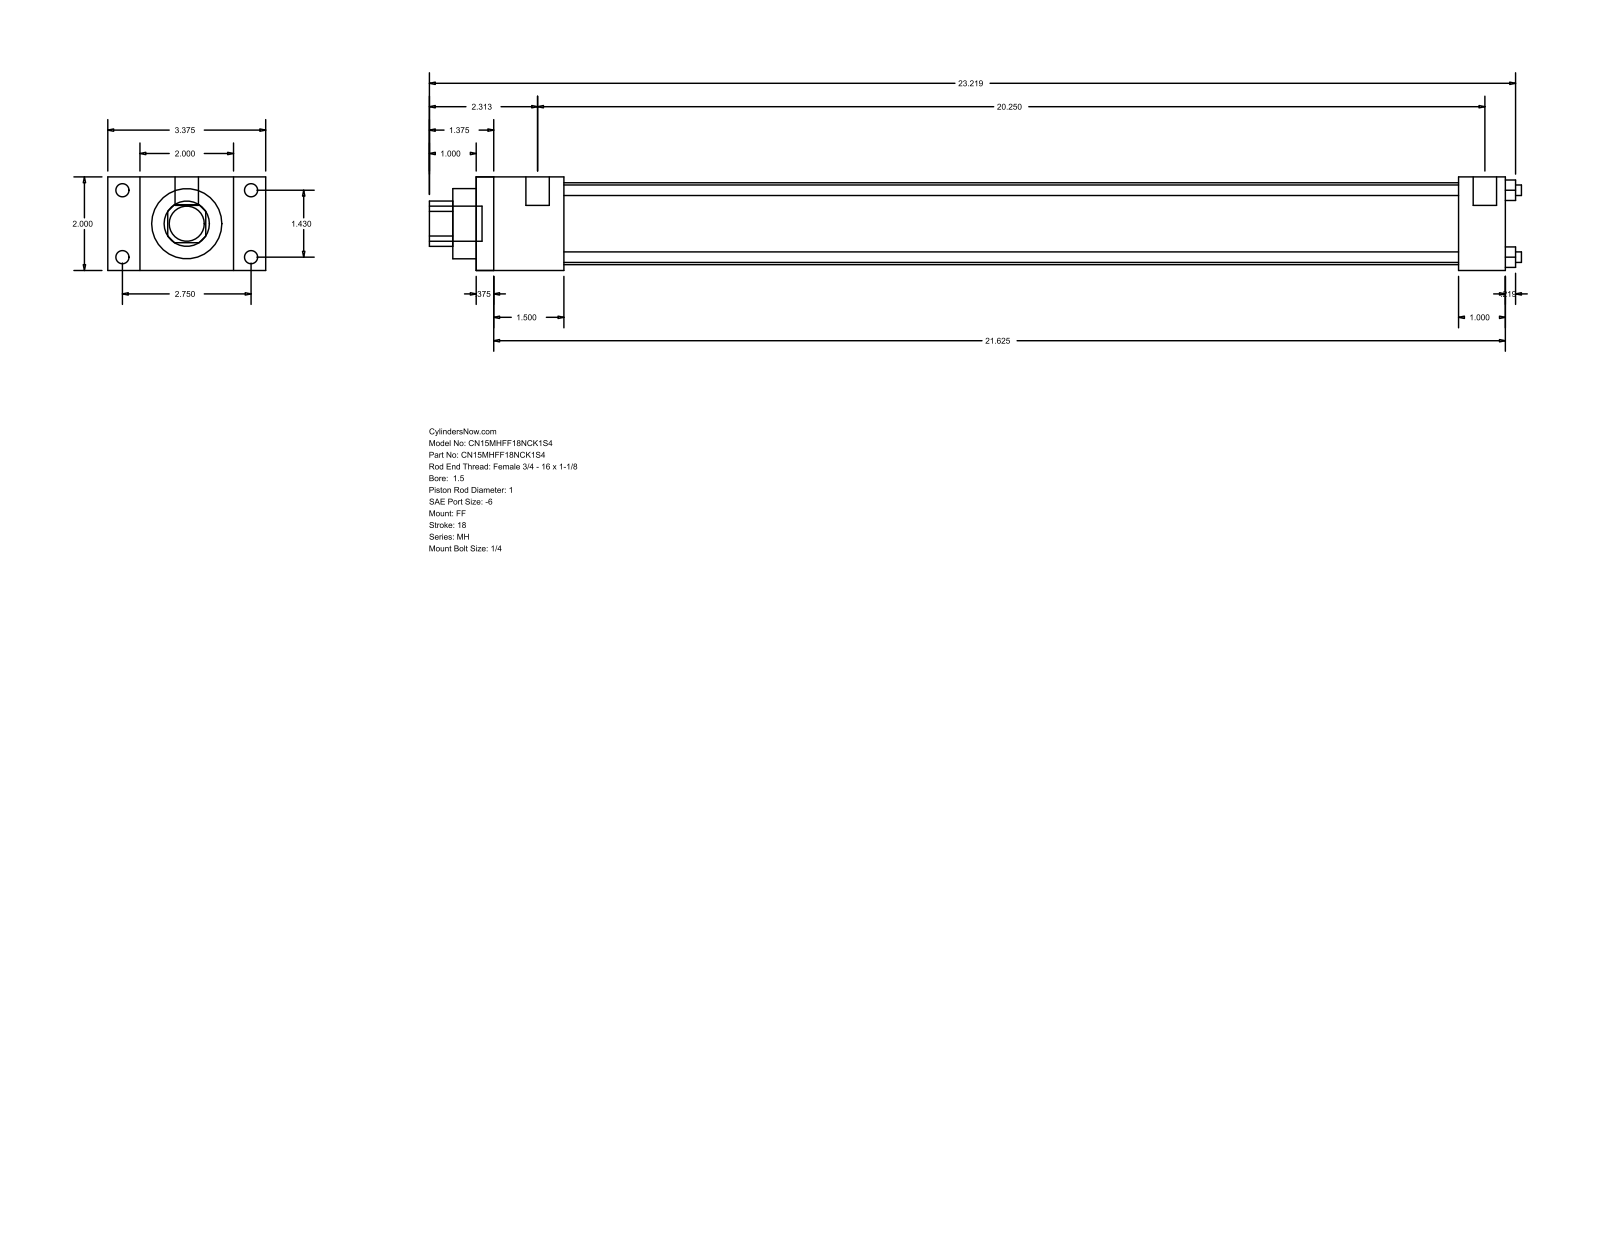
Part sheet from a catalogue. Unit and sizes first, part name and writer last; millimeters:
Units: millimetres
Overall size (bounding box): 592.93 × 85.72 × 50.8
Round holes (diameter × count): ⌀5.71 ×4, ⌀25.4 ×1, ⌀38.1 ×1, ⌀44.45 ×1
Round bosses / shafts (diameter × count): ⌀7.14 ×4, ⌀5.56 ×4, ⌀12.7 ×2, ⌀19.05 ×1
Partial cylindrical surfaces — rounded edges, fillets, slot ends (radius × count): R12.29 ×1
Main face-to-face distances: 50.8, 558.8, 9.52, 549.28, 25.4, 17.46, 68.26, 47.63, 38.11, 511.17
Hole centre spacings: 25.68, 36.32, 51.36
Bodies: 0 solids, 92 faces (64 planar, 28 cylindrical, 0 other)
Part name (STEP PRODUCT): MH_FF__0150_1
STEP written by: GSSL Pune (CONFIG_CONTROL_DESIGN)
